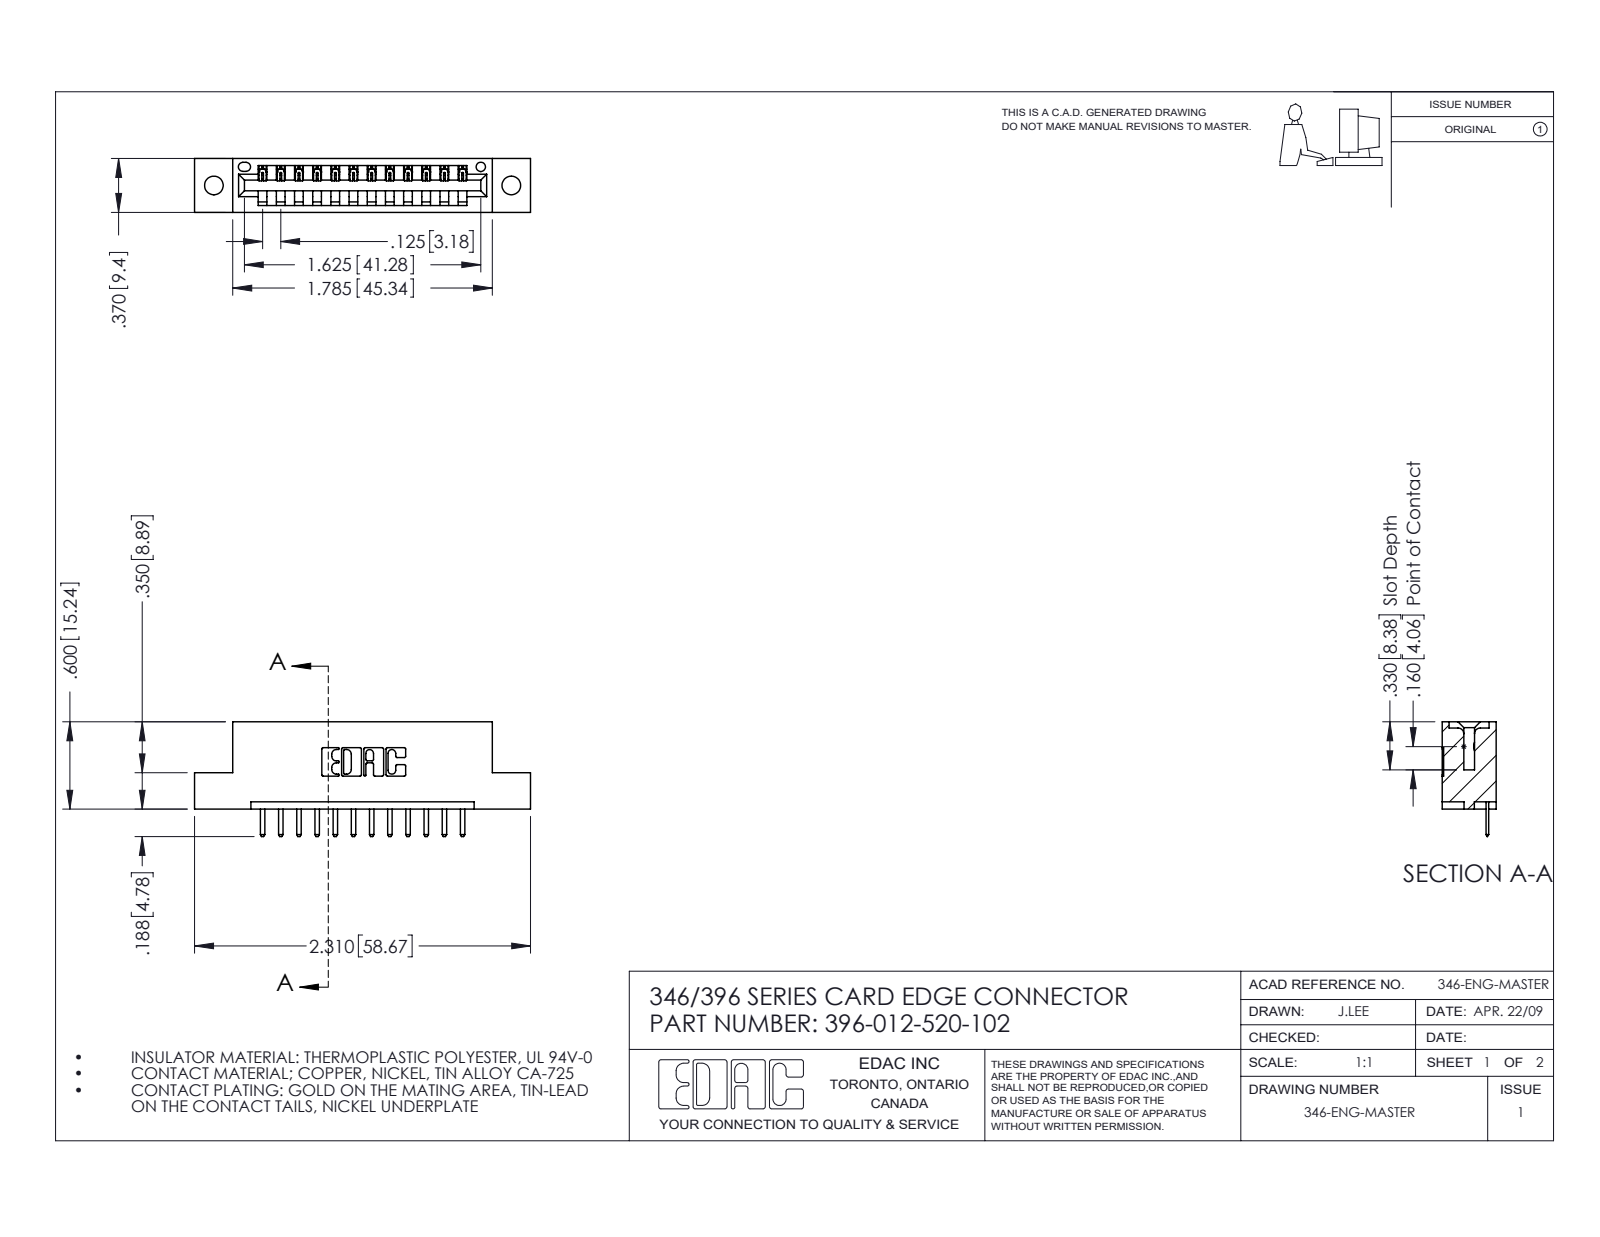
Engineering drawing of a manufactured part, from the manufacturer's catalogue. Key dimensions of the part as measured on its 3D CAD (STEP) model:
Part name (STEP PRODUCT): 346 Part_Flush Mounting Lugs - 0.128 Dia; 345-292-001_345-293-120; 396-012-520-102
STEP written by: SolidWorks 2016 (CONFIG_CONTROL_DESIGN)
Units: inches
Bodies: 13 solids, 866 faces (580 planar, 286 cylindrical, 0 other)
Overall size (bounding box): 2.31 × 0.788 × 0.37
Volume: 0.326 in³ · Surface area: 9.241 in²
Round holes (diameter × count): ⌀0.128 ×2, ⌀0.064 ×1
Partial cylindrical surfaces — rounded edges, fillets, slot ends (radius × count): R0.01 ×26, R0.006 ×24, R0.01 ×22, R0.007 ×6, R0.031 ×6, R0.026 ×3, R0.031 ×2, R0.04 ×2
Main face-to-face distances: 0.25, 0.37, 0.048, 0.322, 0.148, 0.222, 0.1, 0.174, 0.072, 0.298
Hole centre spacings: 0.246, 1.839, 2.045
